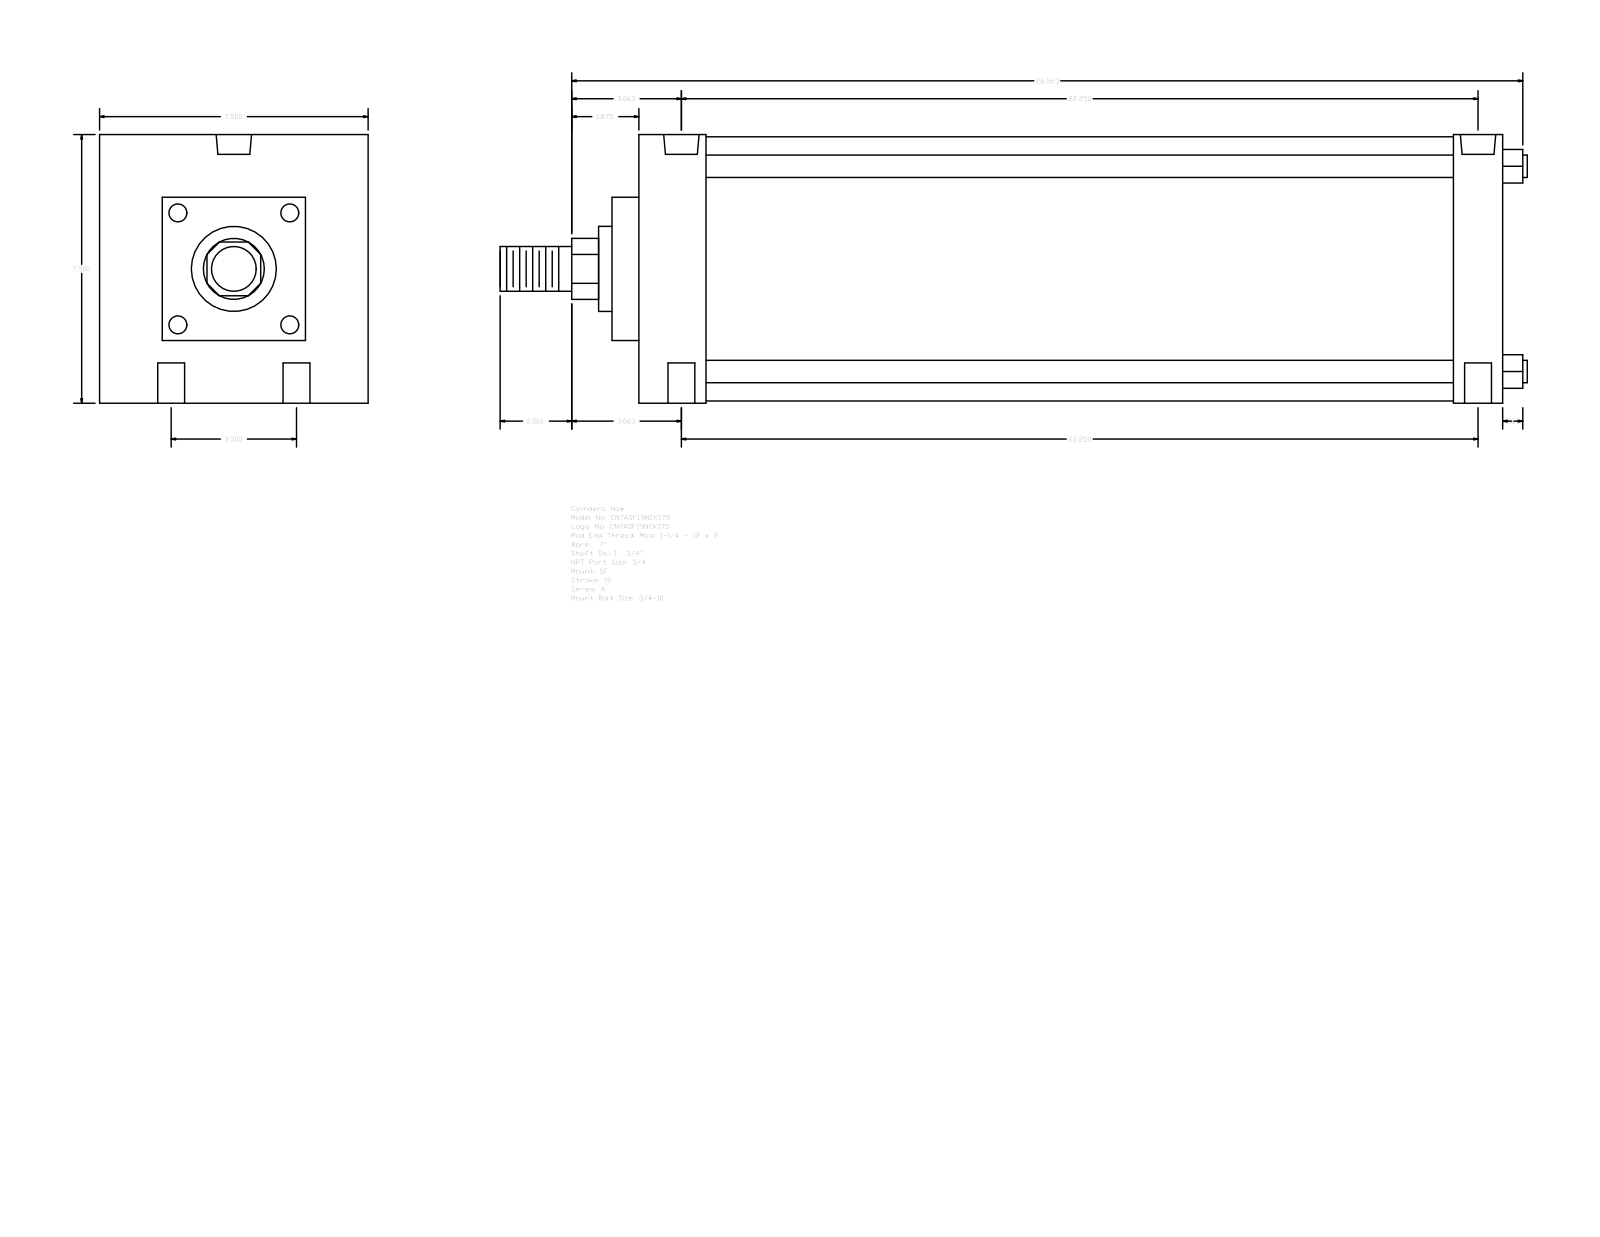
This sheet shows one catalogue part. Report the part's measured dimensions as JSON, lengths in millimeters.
{"part_name": "A_SF__0700_1.75", "step_written_by": "GSSL Pune (CONFIG_CONTROL_DESIGN)", "units": "millimeters", "bodies": {"solids": 0, "faces": 93, "planar": 67, "cylindrical": 26, "other": 0}, "overall_size": [728.66, 190.5, 190.5], "round_holes": [[19.05, 4], [15.08, 2], [25.12, 2]], "round_bosses_or_shafts": [[15.88, 4], [187.32, 1], [60.33, 1], [44.45, 1], [31.75, 1]], "partial_cylinders_radius": [[21.63, 1]], "face_to_face_distances": [190.5, 612.78, 146.05, 19.05, 47.63, 577.86, 530.23, 565.15, 34.92, 44.45], "hole_center_spacings": [44.45, 566.9, 565.15, 88.9, 572.1, 554.03]}
